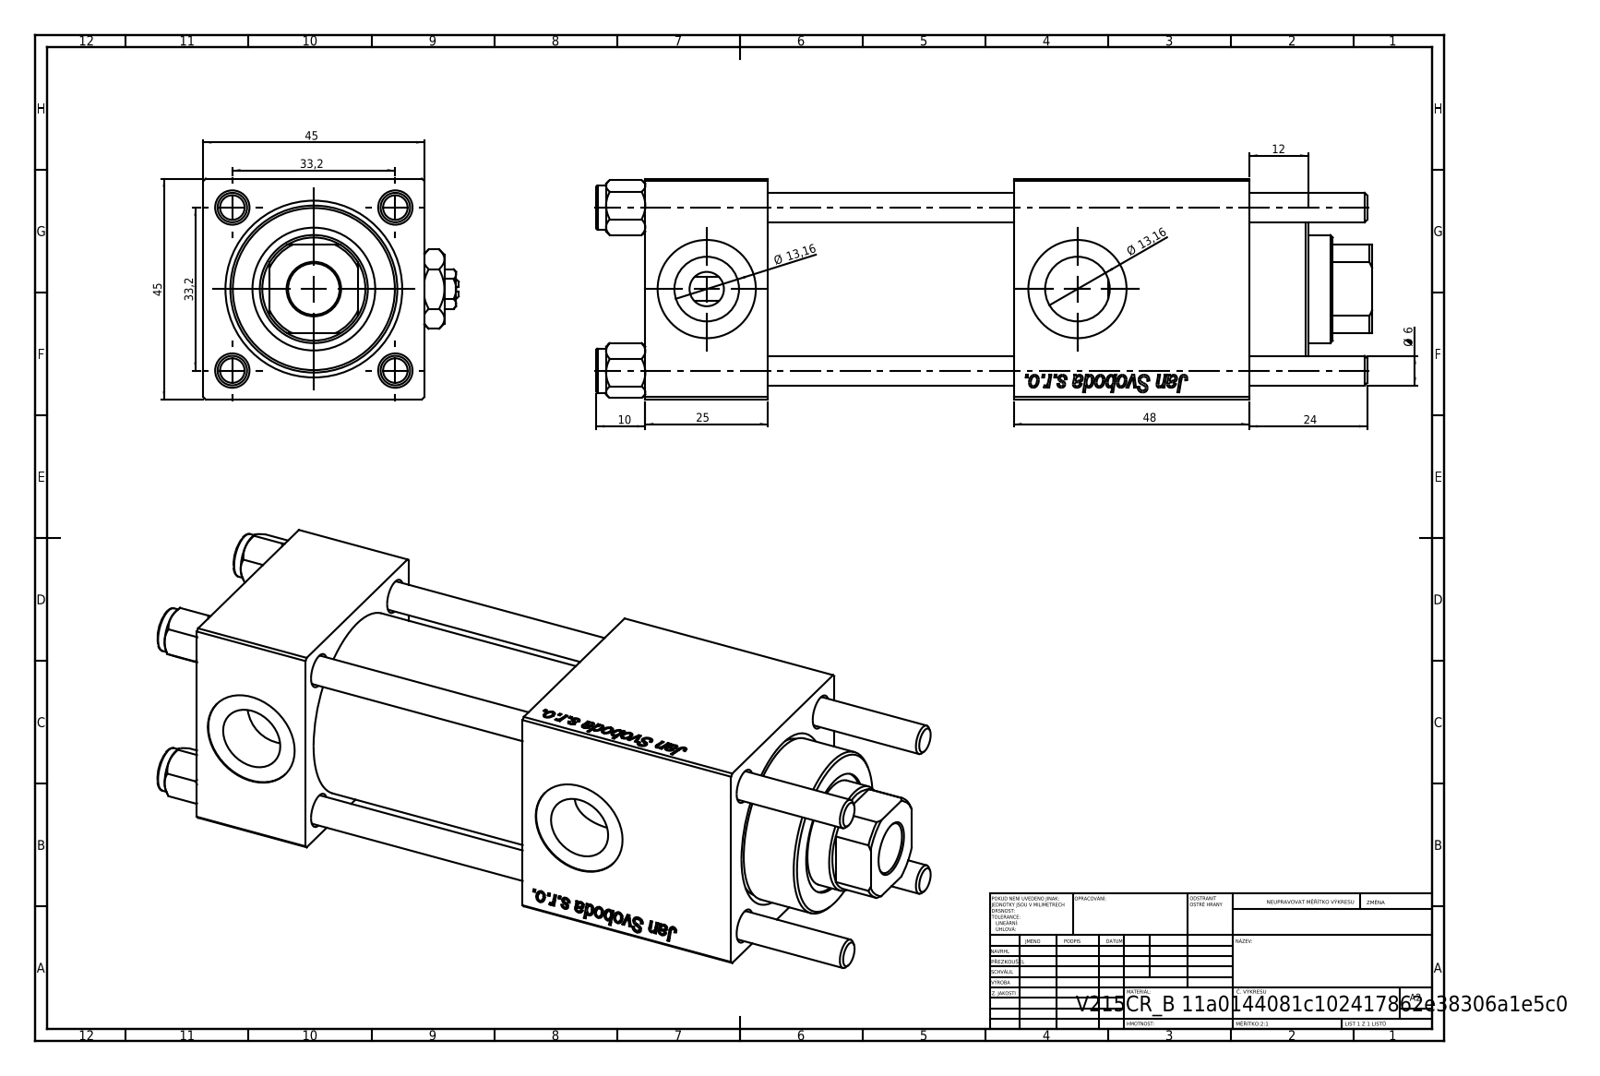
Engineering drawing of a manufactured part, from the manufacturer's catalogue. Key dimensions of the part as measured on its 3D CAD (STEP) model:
Part name (STEP PRODUCT): V215CR_B-1; V215CR_B_TYCINKA; V215CR_VCP_B; V215_VC_A (+2 more)
STEP written by: SolidWorks 2019 (CONFIG_CONTROL_DESIGN)
Units: millimetres
Bodies: 13 solids, 1256 faces (478 planar, 88 cylindrical, 690 other)
Overall size (bounding box): 158 × 52 × 45
Volume: 212 781 mm³ · Surface area: 78 630 mm²
Round holes (diameter × count): ⌀6 ×4, ⌀7 ×2, ⌀13.16 ×2, ⌀20 ×2, ⌀10.5 ×1, ⌀22 ×1, ⌀24 ×1, ⌀25 ×1, ⌀32 ×1, ⌀33 ×1
Round bosses / shafts (diameter × count): ⌀9 ×4, ⌀38 ×1, ⌀34 ×1
Partial cylindrical surfaces — rounded edges, fillets, slot ends (radius × count): R10.5 ×1
Main face-to-face distances: 45, 25, 50, 123, 75, 44.8, 98, 48, 94.3, 69.3
Hole centre spacings: 23.48, 33.2, 46.95, 75.5
